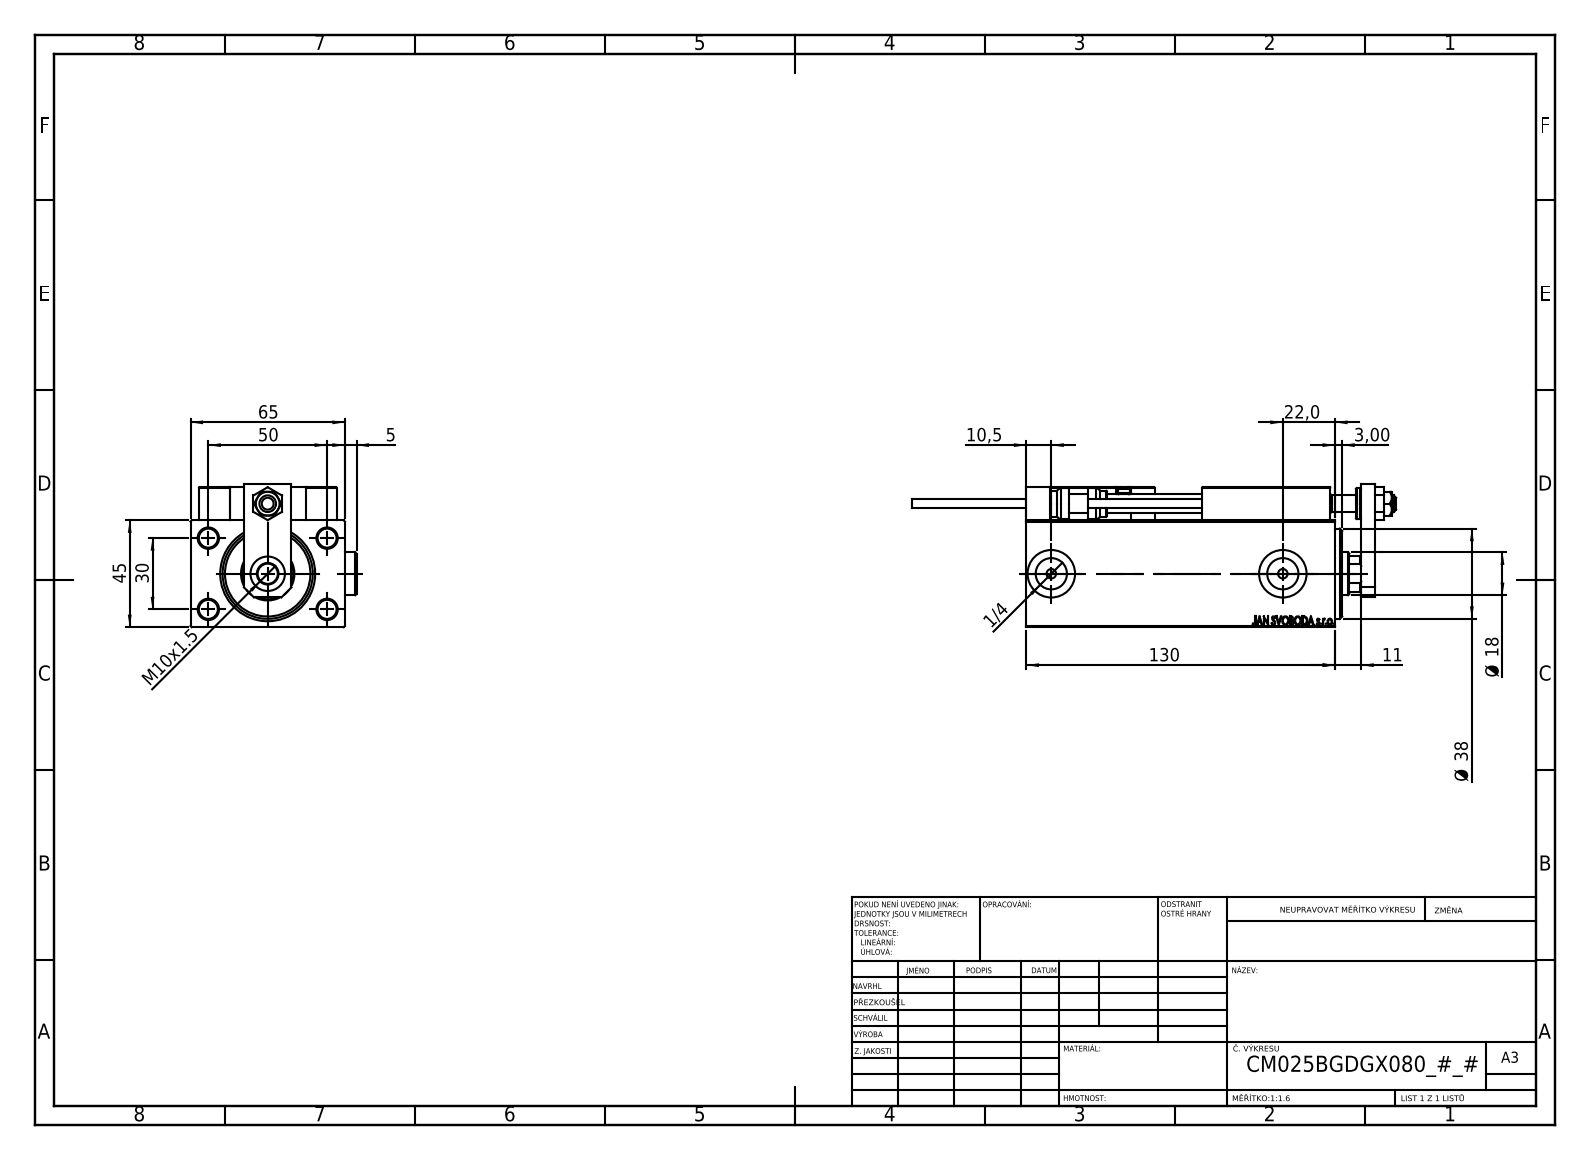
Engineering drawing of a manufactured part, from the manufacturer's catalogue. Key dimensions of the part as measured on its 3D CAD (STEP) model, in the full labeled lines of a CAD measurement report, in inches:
Part name (STEP PRODUCT): SWITCH X; V450CM_B_Body; KONCOVKA; ALLEN BOLT D8 (+8 more)
STEP written by: SolidWorks 2019 (CONFIG_CONTROL_DESIGN)
Units: inches
Bodies: 26 solids, 1372 faces (595 planar, 200 cylindrical, 577 other)
Overall size (bounding box): 8.02 × 2.752 × 2.382
Volume: 24.52 in³ · Surface area: 139.4 in²
Round holes (diameter × count): ⌀0.315 ×9, ⌀0.157 ×6, ⌀0.126 ×4, ⌀0.197 ×2, ⌀0.518 ×2, ⌀0.787 ×2, ⌀0.276 ×1, ⌀0.335 ×1, ⌀0.571 ×1, ⌀0.709 ×1, ⌀0.846 ×1, ⌀0.886 ×1
Round bosses / shafts (diameter × count): ⌀0.709 ×2, ⌀0.197 ×2, ⌀0.15 ×2, ⌀0.512 ×1, ⌀0.433 ×1
Partial cylindrical surfaces — rounded edges, fillets, slot ends (radius × count): R0.012 ×30, R0.118 ×2, R0.335 ×1
Main face-to-face distances: 1.772, 2.559, 0.551, 0.236, 2.323, 0.197, 0.512, 0.138, 5.551, 0.748
Hole centre spacings: 1.148, 0.448, 0.787, 1.138, 1.165, 1.169, 1.181, 1.42
